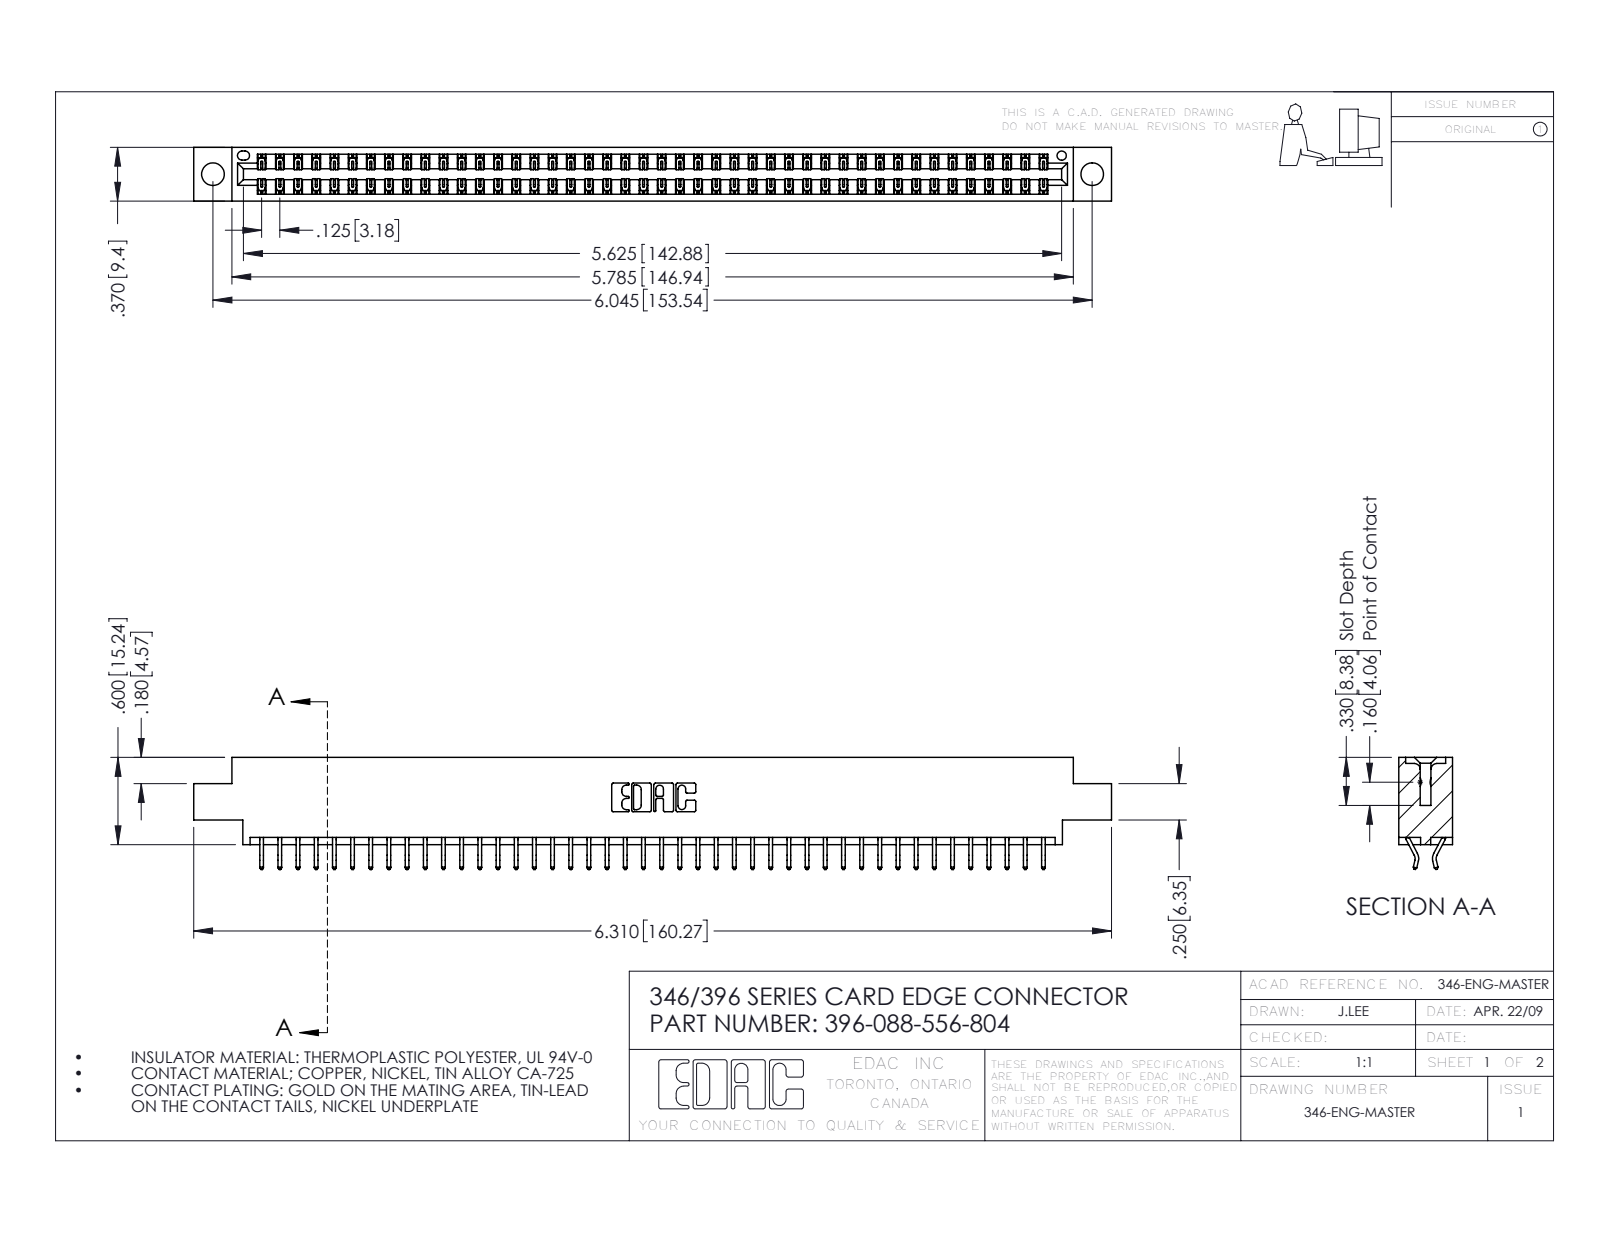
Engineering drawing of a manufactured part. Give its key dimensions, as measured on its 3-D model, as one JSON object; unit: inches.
{"part_name": "345-292-001_556 Tail; 346 Part_0.170 Offset - 0.156 Dia-TH; 396-088-556-804", "step_written_by": "SolidWorks 2016 (CONFIG_CONTROL_DESIGN)", "units": "inches", "bodies": {"solids": 89, "faces": 5230, "planar": 3512, "cylindrical": 1718, "other": 0}, "overall_size": [6.31, 0.77, 0.37], "volume_in3": 0.94, "surface_area_in2": 32.72, "round_holes": [[0.156, 2], [0.064, 1]], "partial_cylinders_radius": [[0.006, 132], [0.01, 22], [0.007, 6], [0.031, 6], [0.026, 3], [0.01, 2], [0.014, 2], [0.022, 2]], "face_to_face_distances": [0.048, 0.322, 0.37, 0.25, 0.025, 0.072, 0.298, 0.275, 0.148, 0.222], "hole_center_spacings": [0.246, 5.836, 6.045]}
